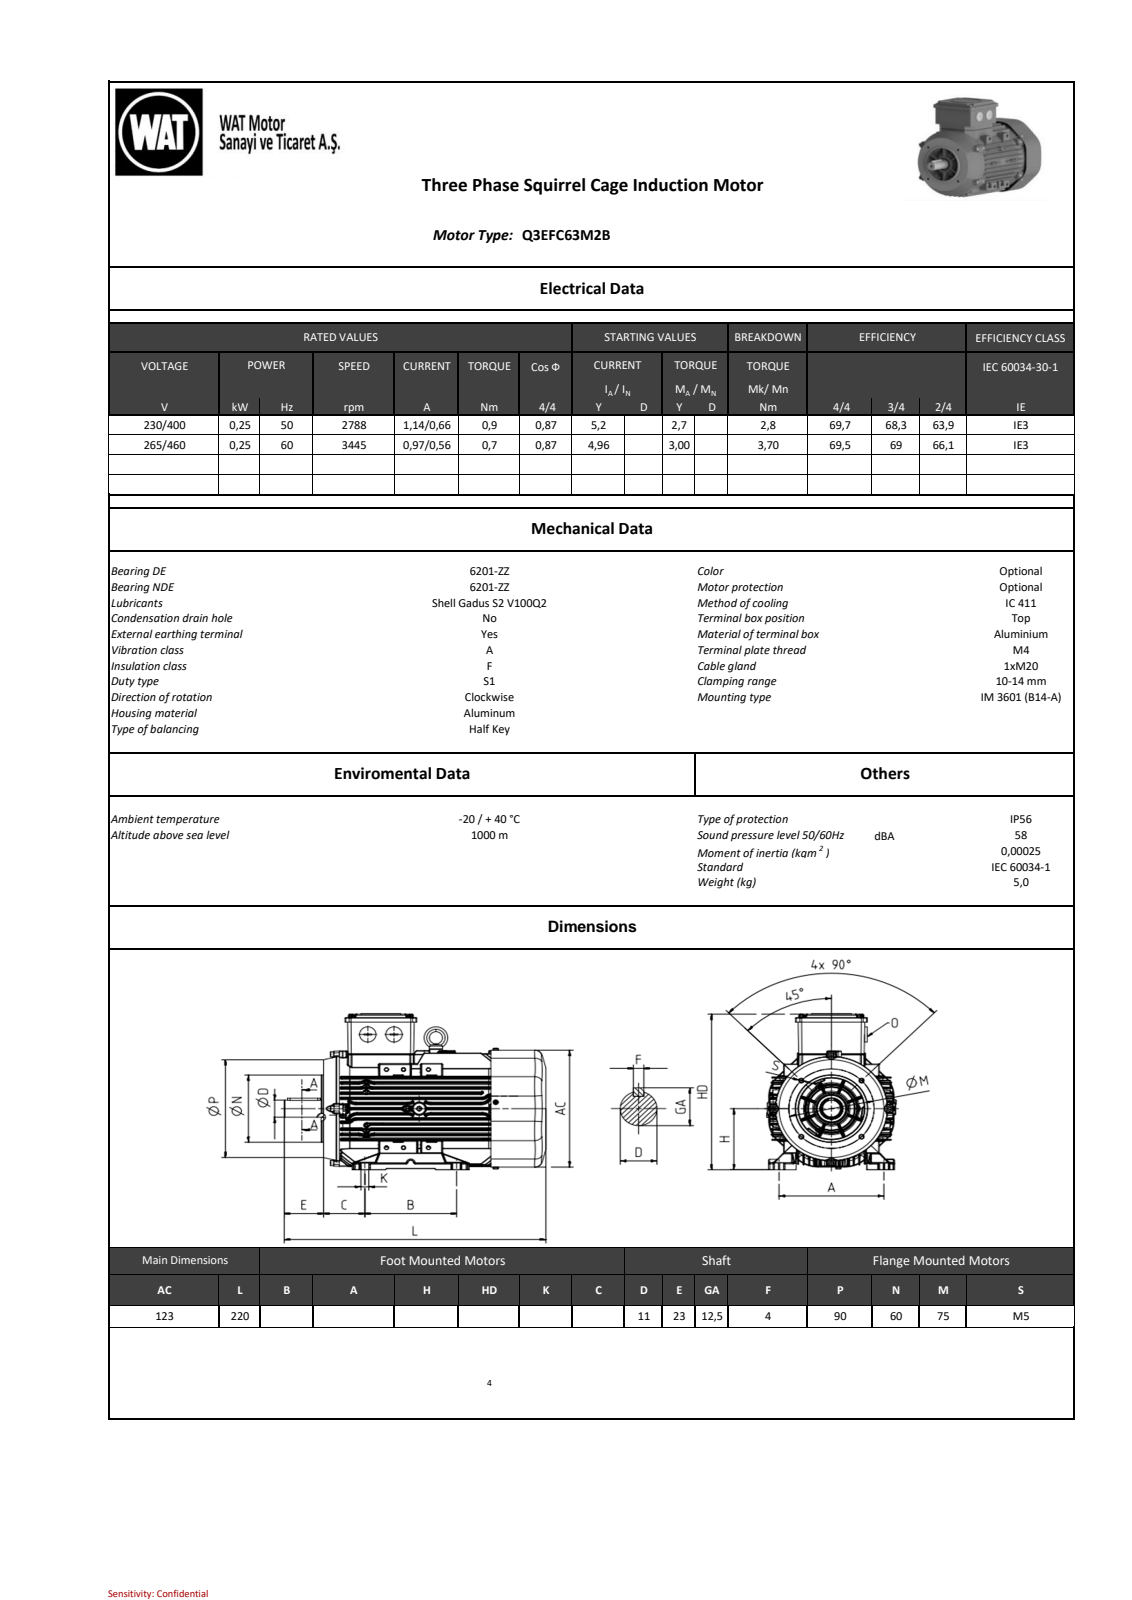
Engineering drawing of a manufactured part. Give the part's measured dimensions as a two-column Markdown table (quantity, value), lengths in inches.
| quantity | value |
| --- | --- |
| part name | QE series_ 63_B14a_stp_objects |
| STEP written by | SIEMENS PLM Software NX2206.8101 (AP203_CONFIGURATION_CONTROLLED_3D_DESIGN_OF_MECHANICAL_PARTS_AND_ASSEMBLIES_MIM_LF) |
| units | inches |
| bodies | 0 solids, 1259 faces (726 planar, 357 cylindrical, 176 other) |
| overall size | 8.628 × 6.283 × 5.039 |
| round holes (diameter × count) | 0.144 × 8, 0.098 × 4, 0.15 × 4, 0.197 × 4, 0.118 × 2, 0.315 × 1, 0.441 × 1, 0.571 × 1 |
| round bosses / shafts (diameter × count) | 0.315 × 8, 0.157 × 4, 4.843 × 1, 4.764 × 1, 2.362 × 1, 1.024 × 1, 0.748 × 1 |
| partial cylindrical surfaces (radius × count) | 0.02 × 101, 0.059 × 28, 0.039 × 23, 0.004 × 14, 0.053 × 12, 0.157 × 12, 0.012 × 6, 0.079 × 6 |
| main face-to-face distances | 1.101, 0.55, 0.557, 0.273, 0.271, 0.828, 0.276, 0.823, 0.278, 1.38 |
| hole center spacings | 1.476, 2.126, 2.48, 3.267, 0.394, 0.197, 0.667, 1.24 |
